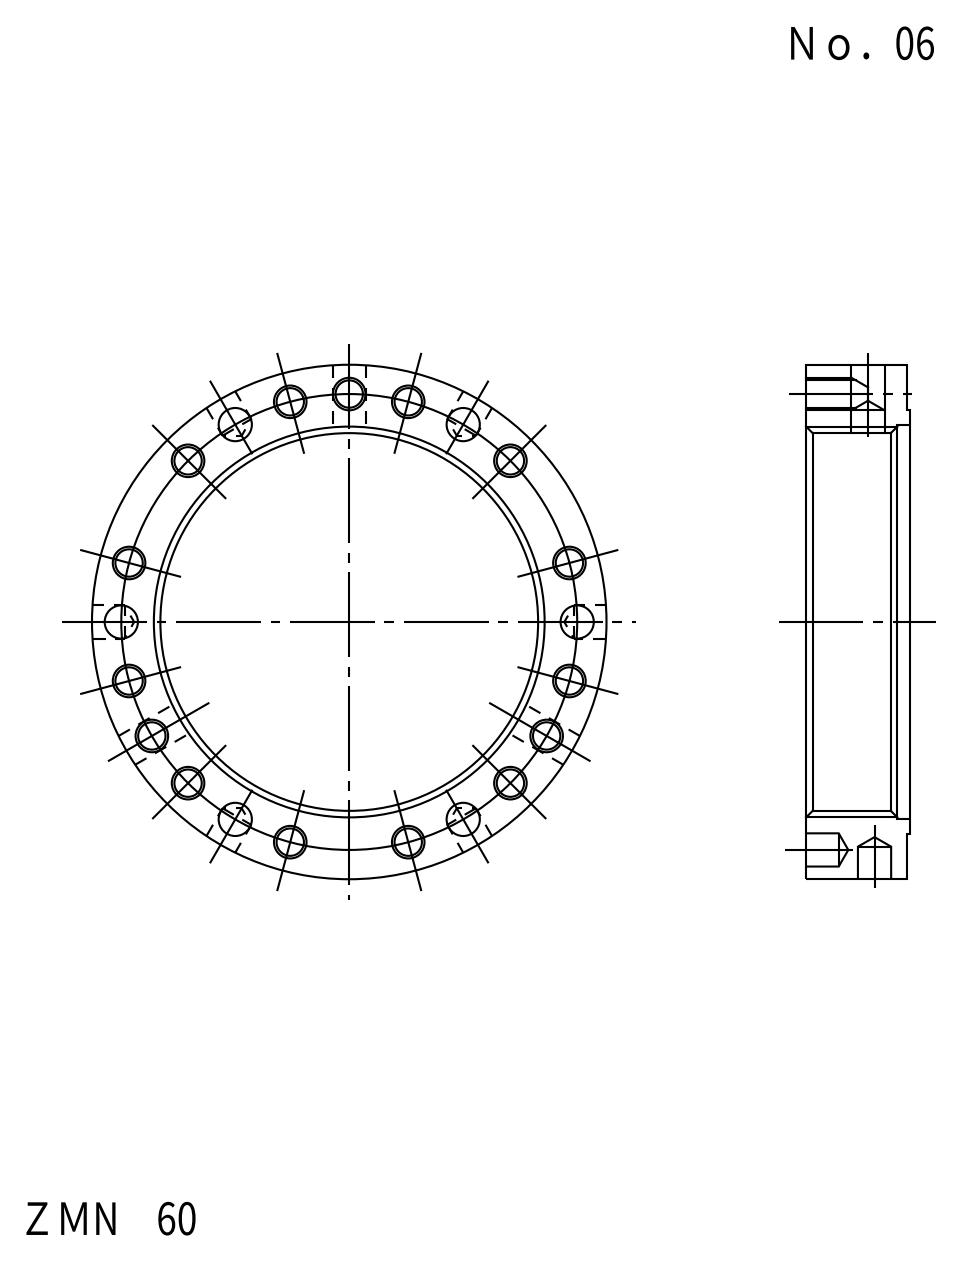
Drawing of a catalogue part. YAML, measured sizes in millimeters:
part_name: "FKD ZMN60"
step_written_by: "Autodesk Inventor LT (CONFIG_CONTROL_DESIGN)"
units: millimeters
bodies: {solids: 1, faces: 62, planar: 4, cylindrical: 34, other: 24}
overall_size: [79, 79, 16]
volume: 28429
surface_area: 14239
round_holes:
  - {diameter: 4.13, count: 15}
  - {diameter: 5.1, count: 12}
  - {diameter: 60, count: 1}
  - {diameter: 60.5, count: 1}
round_bosses_or_shafts:
  - {diameter: 79, count: 1}
  - {diameter: 65, count: 1}
face_to_face_distances: [15.5, 0.5, 16, 1.5, 1, 14.5]
hole_center_spacings: [35, 9.14, 18.12, 26.79, 42.61, 49.5, 55.54, 64.67]
